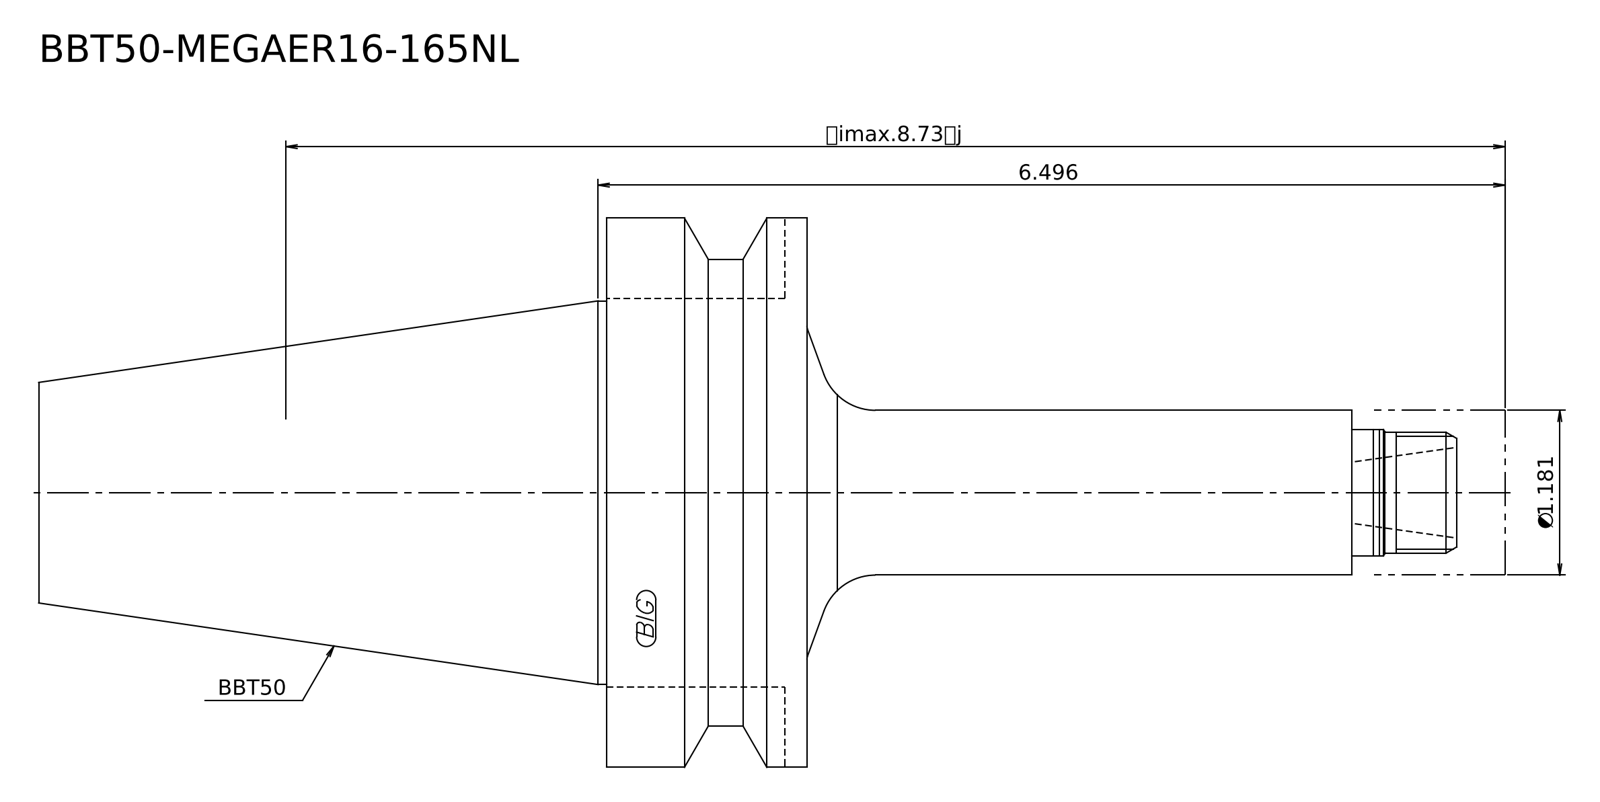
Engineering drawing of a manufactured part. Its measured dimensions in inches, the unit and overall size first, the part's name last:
Units: inches
Overall size (bounding box): 10.504 × 3.937 × 3.937
Round bosses / shafts (diameter × count): ⌀3.937 ×1, ⌀3.346 ×1, ⌀2.75 ×1, ⌀1.181 ×1, ⌀0.906 ×1, ⌀0.866 ×1
Main face-to-face distances: 1.437, 5.504, 4.067, 4.016, 5.453, 9.52, 0.984, 5, 6.437, 10.504
Volume: 38.07 in³ · Surface area: 90.77 in²
Bodies: 2 solids, 21 faces (7 planar, 8 cylindrical, 6 other)
STEP written by: Kubotek KeyCreator 2011 V10.0.2 (22737) (automotive_design)
